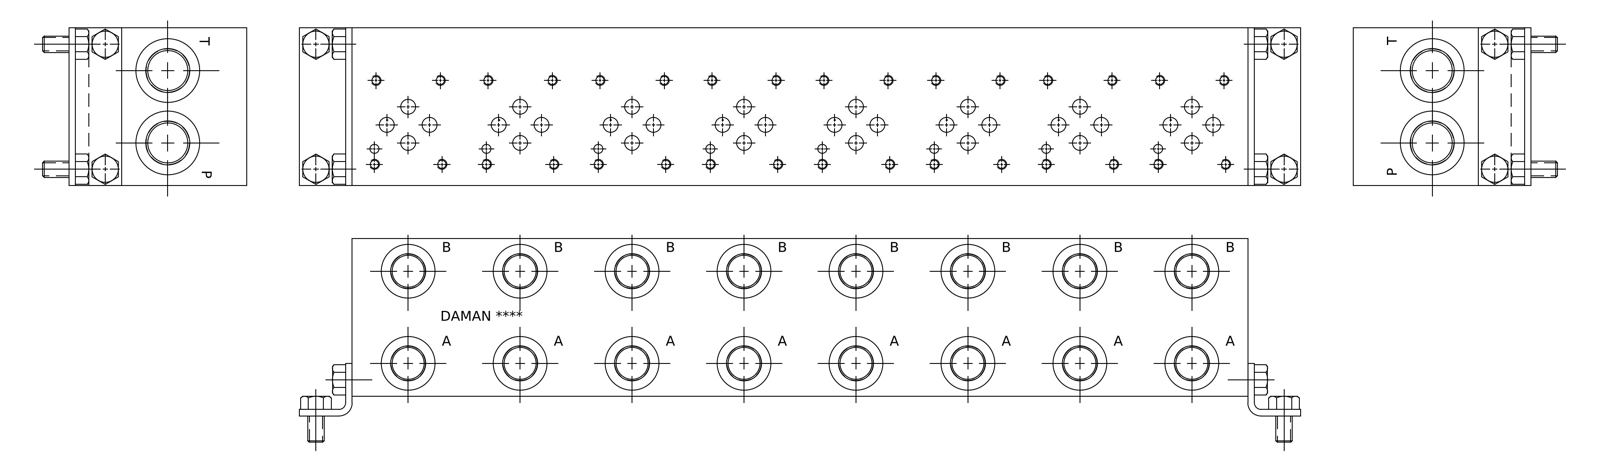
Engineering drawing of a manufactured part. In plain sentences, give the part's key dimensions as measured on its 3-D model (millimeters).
The part is named "Part_AD03P082B_3D". Its 3-D file was written by "Autodesk Inventor 2020 (AUTOMOTIVE_DESIGN)". It is 1 solid with 1085 faces: 538 planar, 192 cylindrical and 355 other. Overall it measures 431.8 by 76.2 by 76.2 millimeters. Its volume is 2 382 000 cubic millimeters and its surface area 180 328 square millimeters. Round holes: 32 of diameter 4.22, 32 of diameter 5, 24 of diameter 7.14, 16 of diameter 14.3, 16 of diameter 15.06, 16 of diameter 16.76, 16 of diameter 25.93, 8 of diameter 3.96, 8 of diameter 6.35, 2 of diameter 6.76, 2 of diameter 8, 2 of diameter 15.88. The main face-to-face distances are 76.2, 0.79, 75.41, 431.8, 431.01, 430.22, 12.98, 12.19, 63.22, 0.75. The hole center spacings are 107.95, 53.98, 215.9, 53.97, 40.49, 51.45, 161.93, 46.18.
